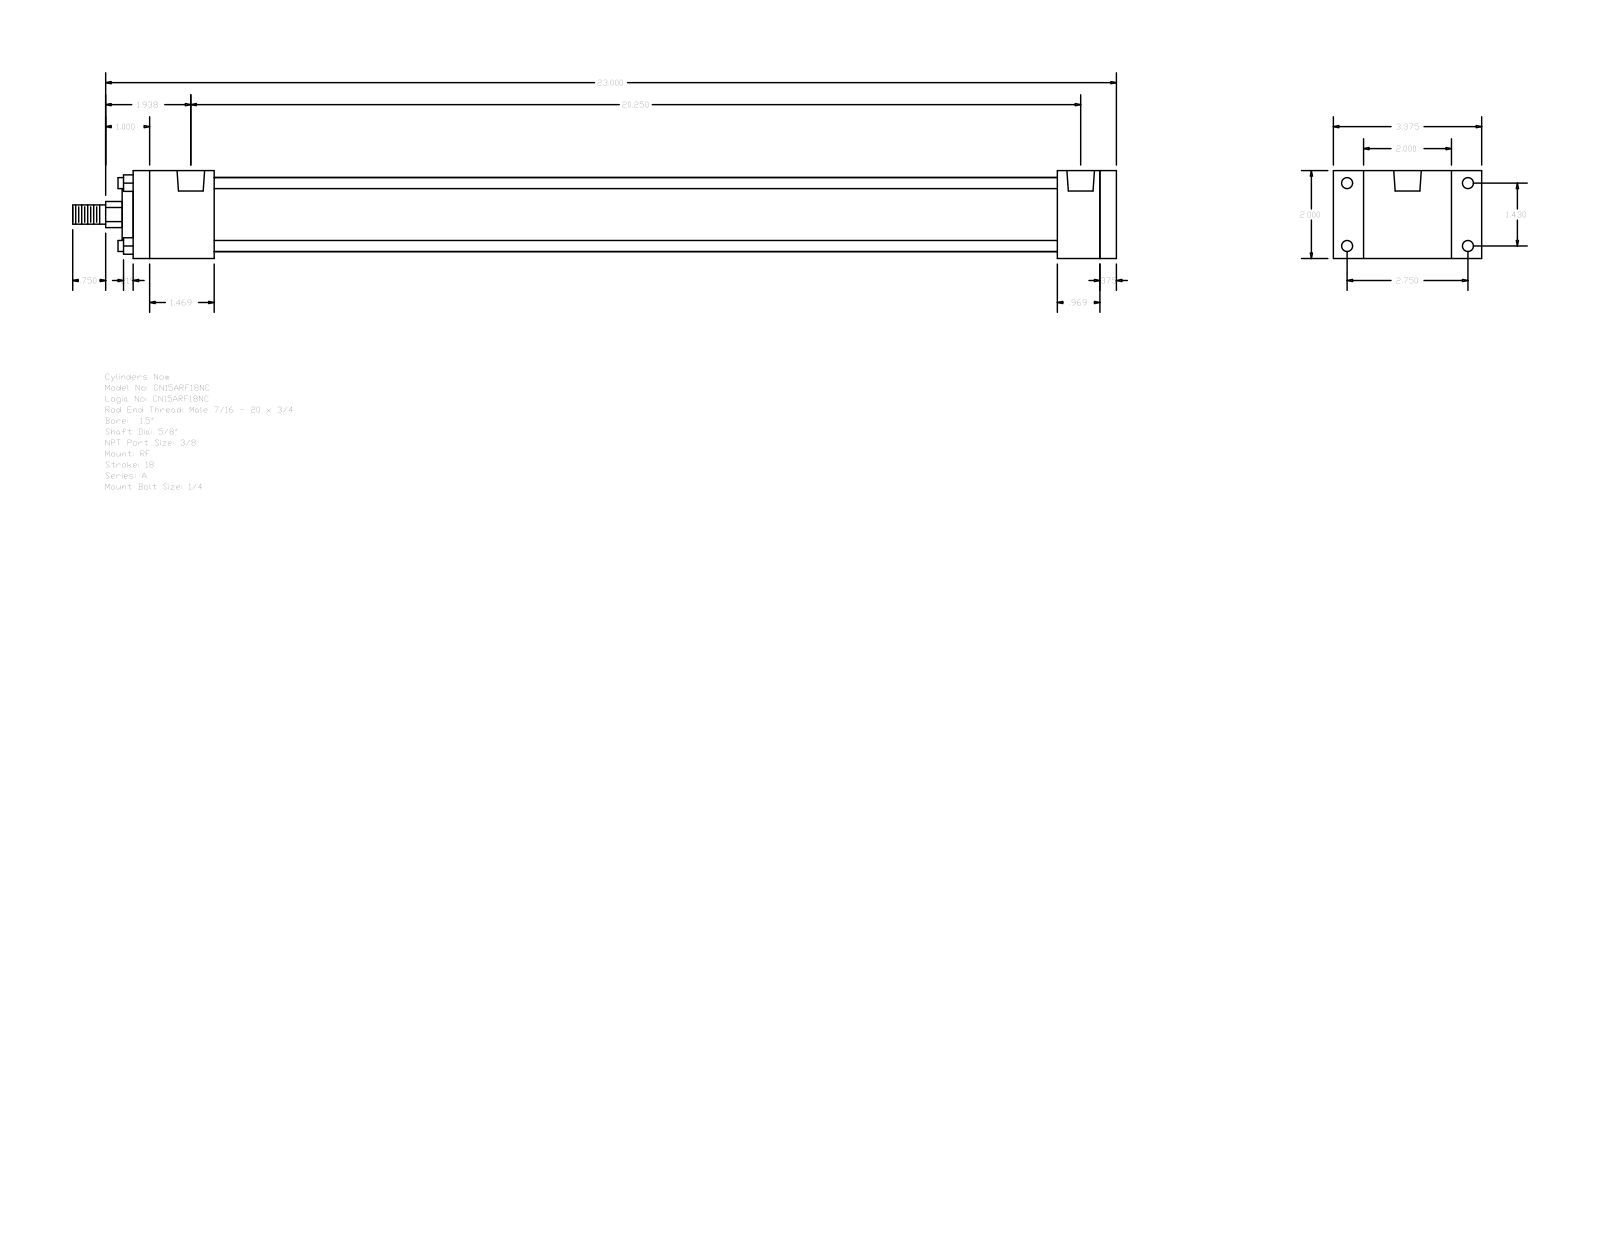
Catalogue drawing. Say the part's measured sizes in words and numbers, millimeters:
The part is named "A_RF__0150_0.625". Its 3-D file was written by "GSSL Pune (CONFIG_CONTROL_DESIGN)". It is 0 solids with 92 faces: 64 planar, 28 cylindrical and 0 other. Overall it measures 603.25 by 85.72 by 50.8 millimeters. Round holes: 4 of diameter 5.56, 4 of diameter 6.35, 2 of diameter 15.93. Round bosses or shafts: 4 of diameter 6.35, 1 of diameter 42.93, 1 of diameter 28.57, 1 of diameter 15.88, 1 of diameter 11.11. Partial cylindrical surfaces (rounded edges, fillets, slot ends): 1 of radius 7.54. The main face-to-face distances are 50.8, 9.53, 568.32, 558.79, 534.19, 24.6, 34.13, 46.83, 487.36, 511.96. The hole center spacings are 3.97, 36.32, 69.84, 78.72, 506.41, 510.38, 514.35.
